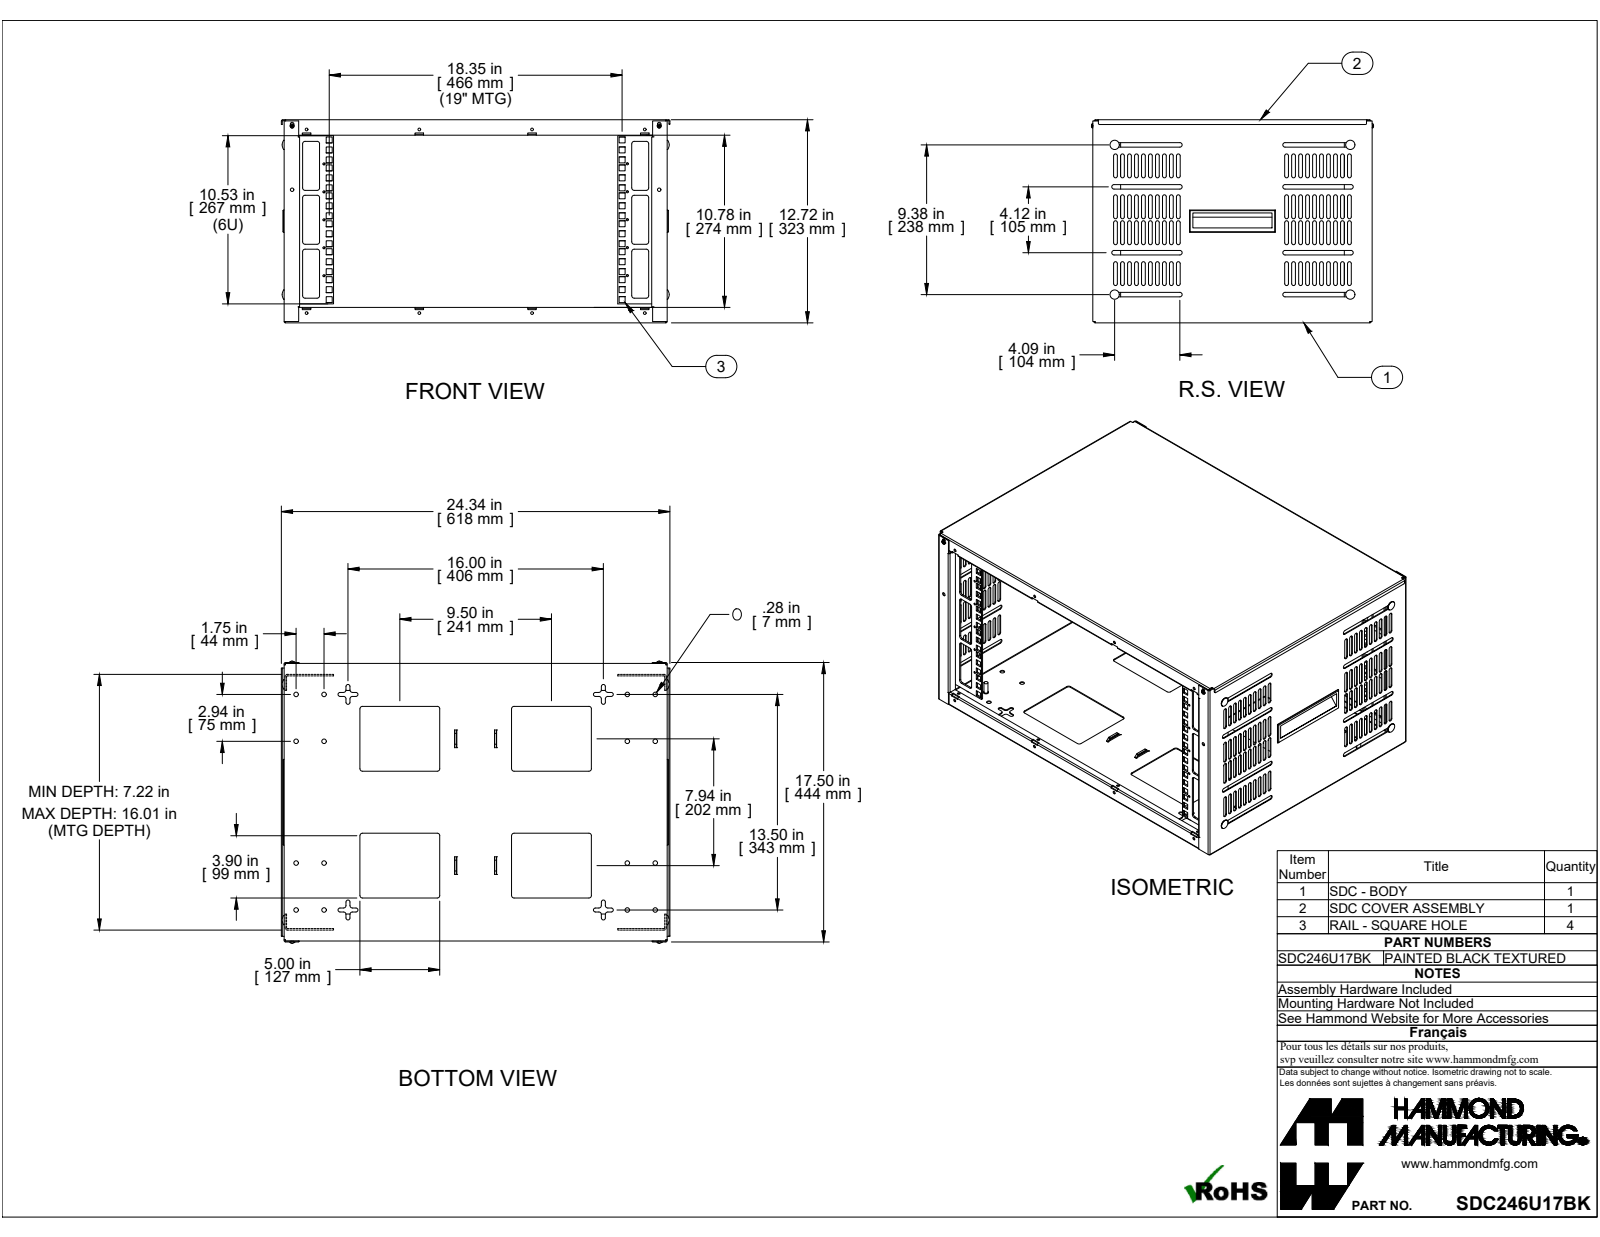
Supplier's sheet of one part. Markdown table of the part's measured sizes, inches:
| quantity | value |
| --- | --- |
| part name | SDC246U17BK |
| STEP written by | SolidWorks 2019 (CONFIG_CONTROL_DESIGN) |
| units | inches |
| bodies | 36 solids, 2302 faces (1470 planar, 780 cylindrical, 52 other) |
| overall size | 24.344 × 17.67 × 12.722 |
| volume | 93.6 in³ |
| surface area | 3 149 in² |
| round holes (diameter × count) | 0.125 × 20, 0.17 × 16, 0.281 × 16, 0.196 × 4, 0.159 × 2, 0.187 × 2, 0.213 × 2 |
| round bosses / shafts (diameter × count) | 0.25 × 8, 0.58 × 4, 0.313 × 2, 0.28 × 2, 0.187 × 2, 0.138 × 2 |
| partial cylindrical surfaces (radius × count) | 0.118 × 152, 0.157 × 60, 0.029 × 22, 0.086 × 22, 0.025 × 16, 0.125 × 16, 0.141 × 16, 0.03 × 8 |
| main face-to-face distances | 0.057, 12.665, 23.943, 12.608, 12.722, 23.886, 24, 0.912, 0.072, 0.095 |
| hole center spacings | 19.085, 1.75, 19.005, 19.324, 3.5, 2.937, 3.419, 7.063 |
